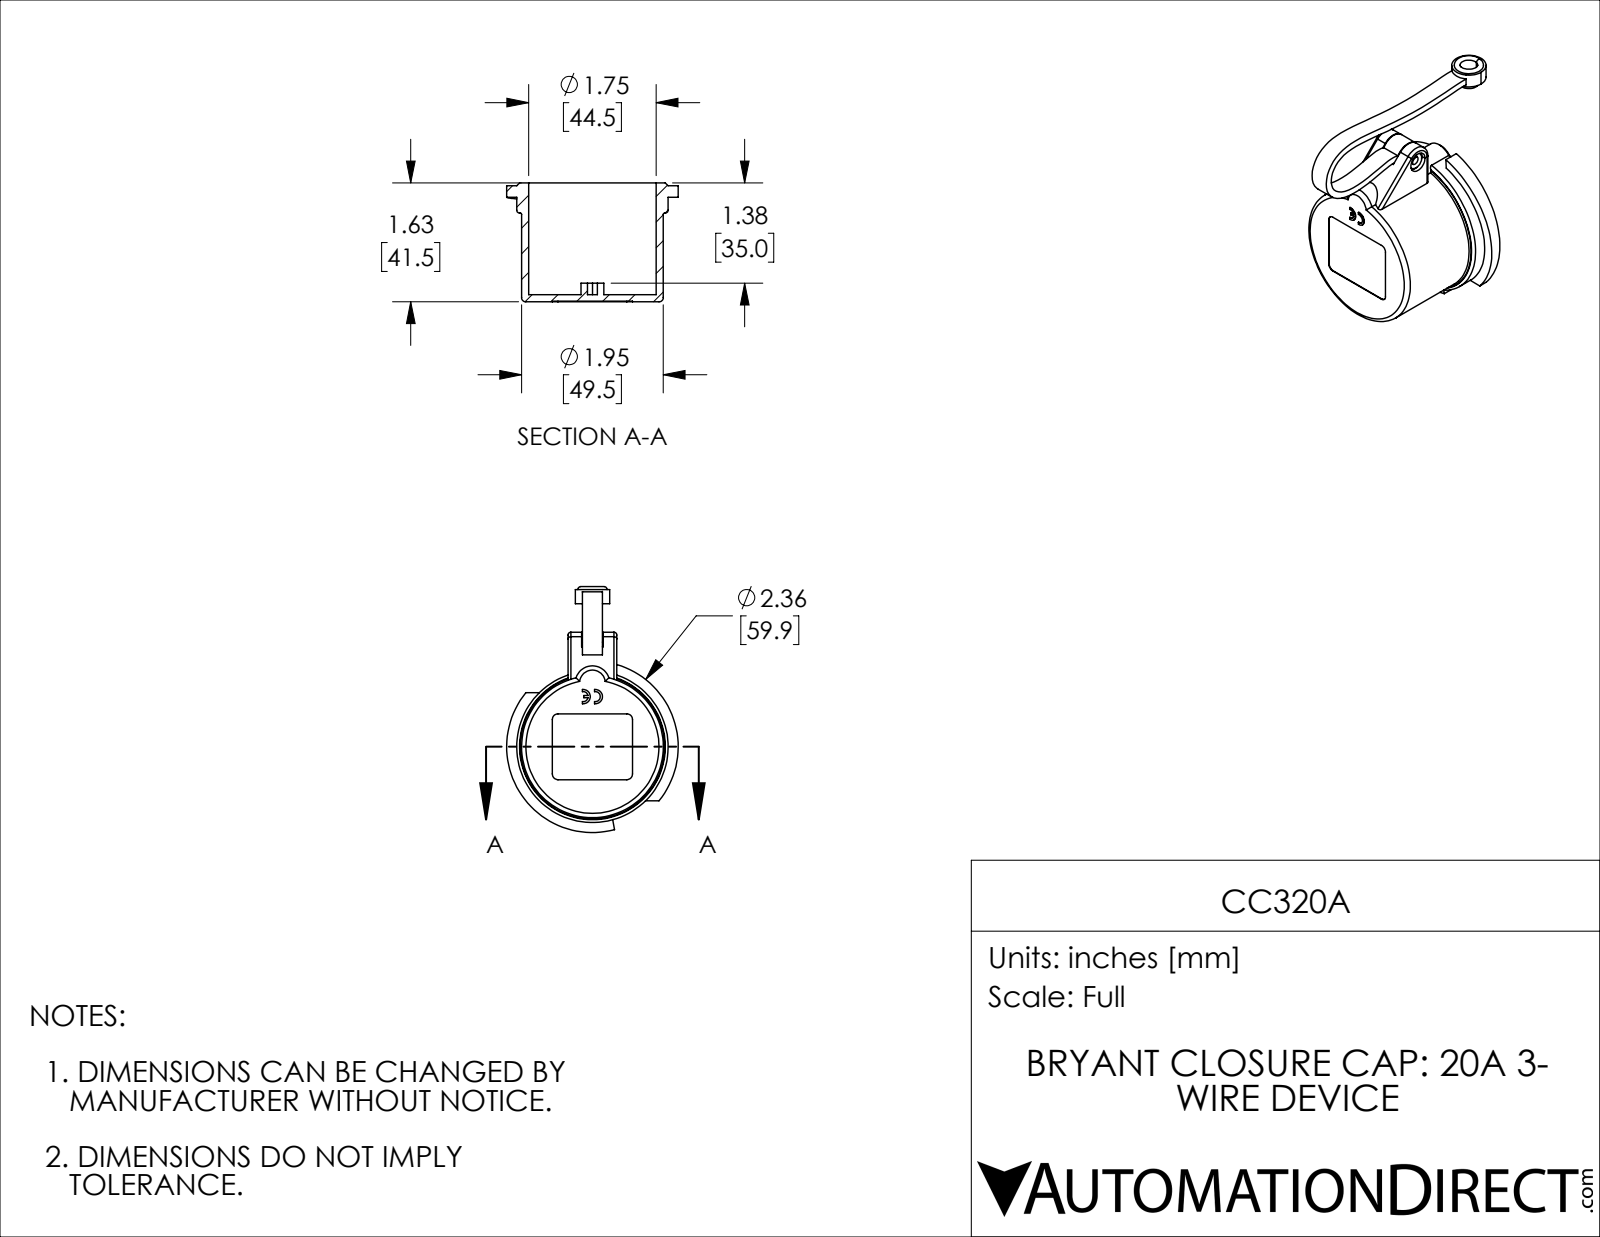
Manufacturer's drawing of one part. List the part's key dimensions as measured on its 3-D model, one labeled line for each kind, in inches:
Part name (STEP PRODUCT): CC320A
STEP written by: SolidWorks 2021 (CONFIG_CONTROL_DESIGN)
Units: inches
Bodies: 1 solid, 149 faces (50 planar, 71 cylindrical, 28 other)
Overall size (bounding box): 3.38 × 3.149 × 2.358
Volume: 1.793 in³ · Surface area: 34.33 in²
Round holes (diameter × count): ⌀0.118 ×1, ⌀0.138 ×1, ⌀0.169 ×1, ⌀0.197 ×1, ⌀0.244 ×1, ⌀0.276 ×1, ⌀1.752 ×1
Round bosses / shafts (diameter × count): ⌀2.083 ×1, ⌀1.949 ×1, ⌀0.472 ×1, ⌀0.433 ×1, ⌀0.315 ×1, ⌀0.276 ×1, ⌀0.236 ×1, ⌀0.157 ×1
Partial cylindrical surfaces — rounded edges, fillets, slot ends (radius × count): R0.039 ×4, R0.079 ×4, R0.069 ×2, R0.098 ×2, R0.138 ×1, R0.236 ×1, R1.179 ×1
Main face-to-face distances: 0.098, 0.091, 1.634, 1.626, 1.535, 0.039, 1.594, 1.587, 1.496, 0.197
